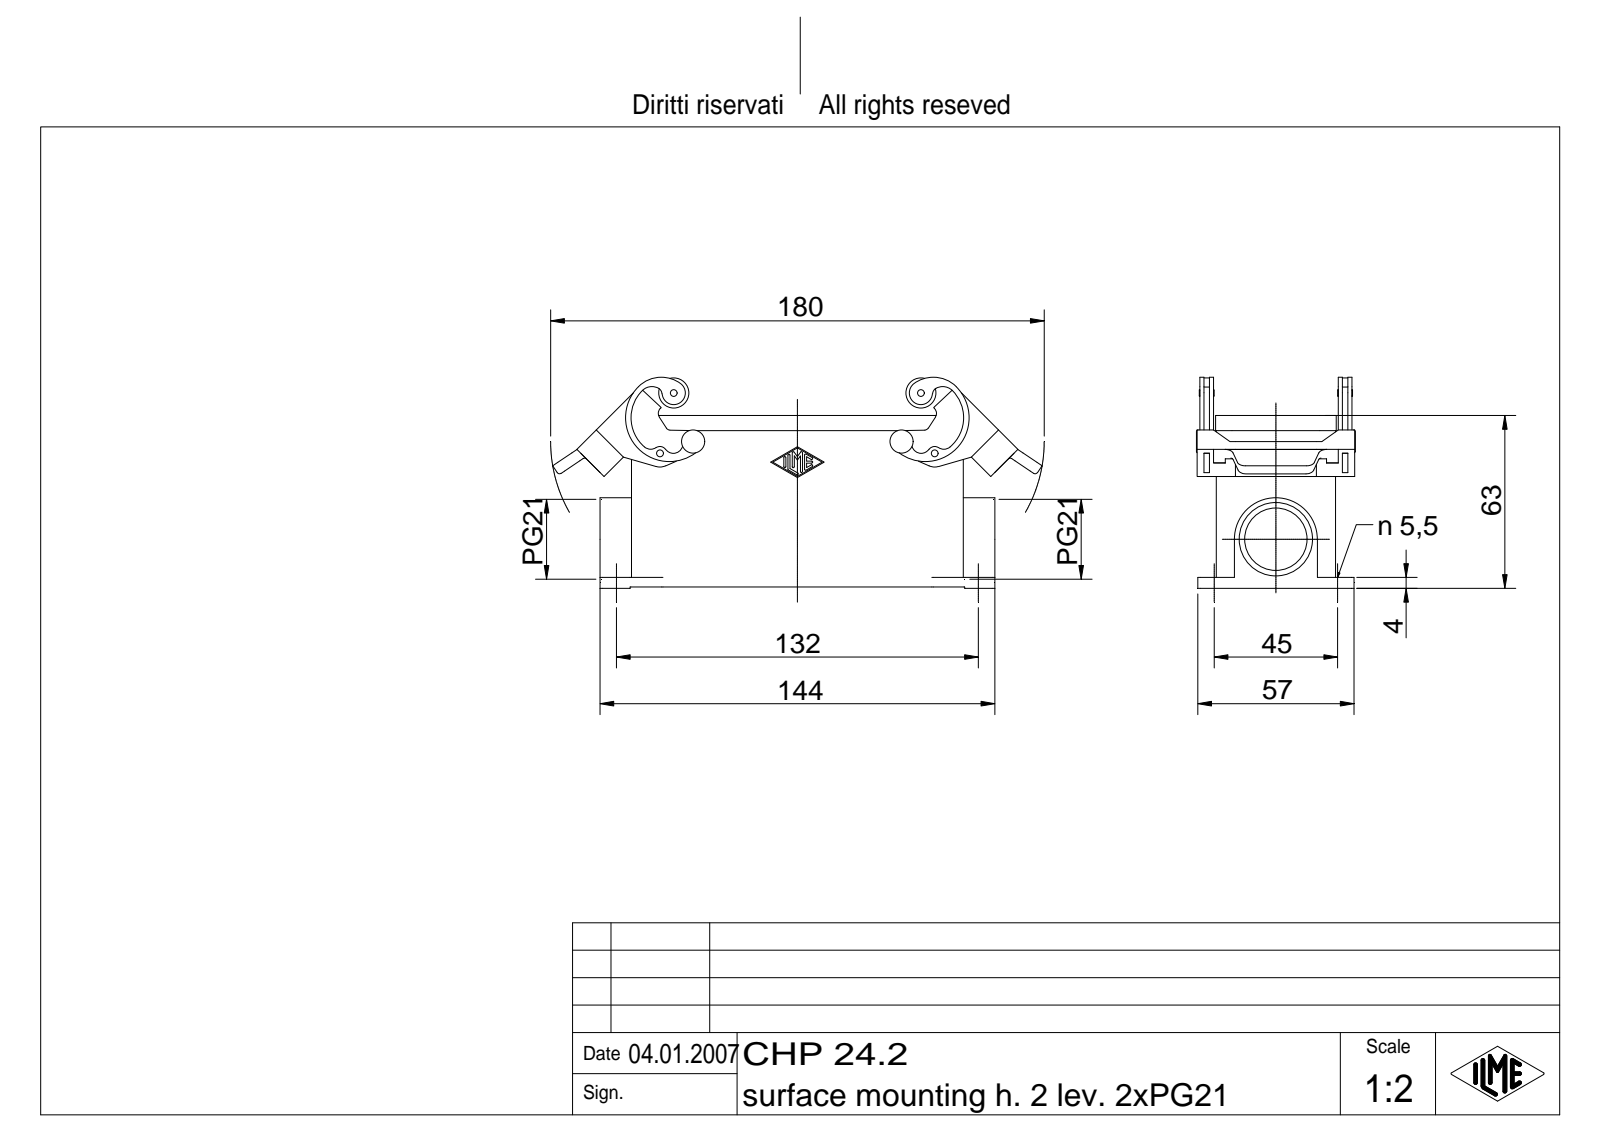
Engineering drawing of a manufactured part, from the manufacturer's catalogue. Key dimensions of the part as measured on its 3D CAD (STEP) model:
Part name (STEP PRODUCT): CHP 24.2
STEP written by: Autodesk Inventor 7 (AUTOMOTIVE_DESIGN)
Units: millimetres
Bodies: 1 solid, 748 faces (191 planar, 205 cylindrical, 352 other)
Overall size (bounding box): 178.49 × 76.94 × 58
Volume: 118 926 mm³ · Surface area: 70 697 mm²
Round holes (diameter × count): ⌀2 ×4, ⌀5.5 ×4, ⌀2.5 ×2, ⌀22.78 ×1, ⌀26.78 ×1
Round bosses / shafts (diameter × count): ⌀11 ×2, ⌀5 ×2, ⌀3 ×2
Partial cylindrical surfaces — rounded edges, fillets, slot ends (radius × count): R1 ×20, R0.38 ×14, R3 ×12, R6 ×8, R2.5 ×6, R1.5 ×4, R2 ×4, R3.5 ×4
Main face-to-face distances: 3, 40.5, 43.5, 37.5, 3.5, 4, 0.75, 50.5, 40.75, 3.75
Hole centre spacings: 22.56, 45, 97.67, 132, 139.46, 90.14, 100.18
